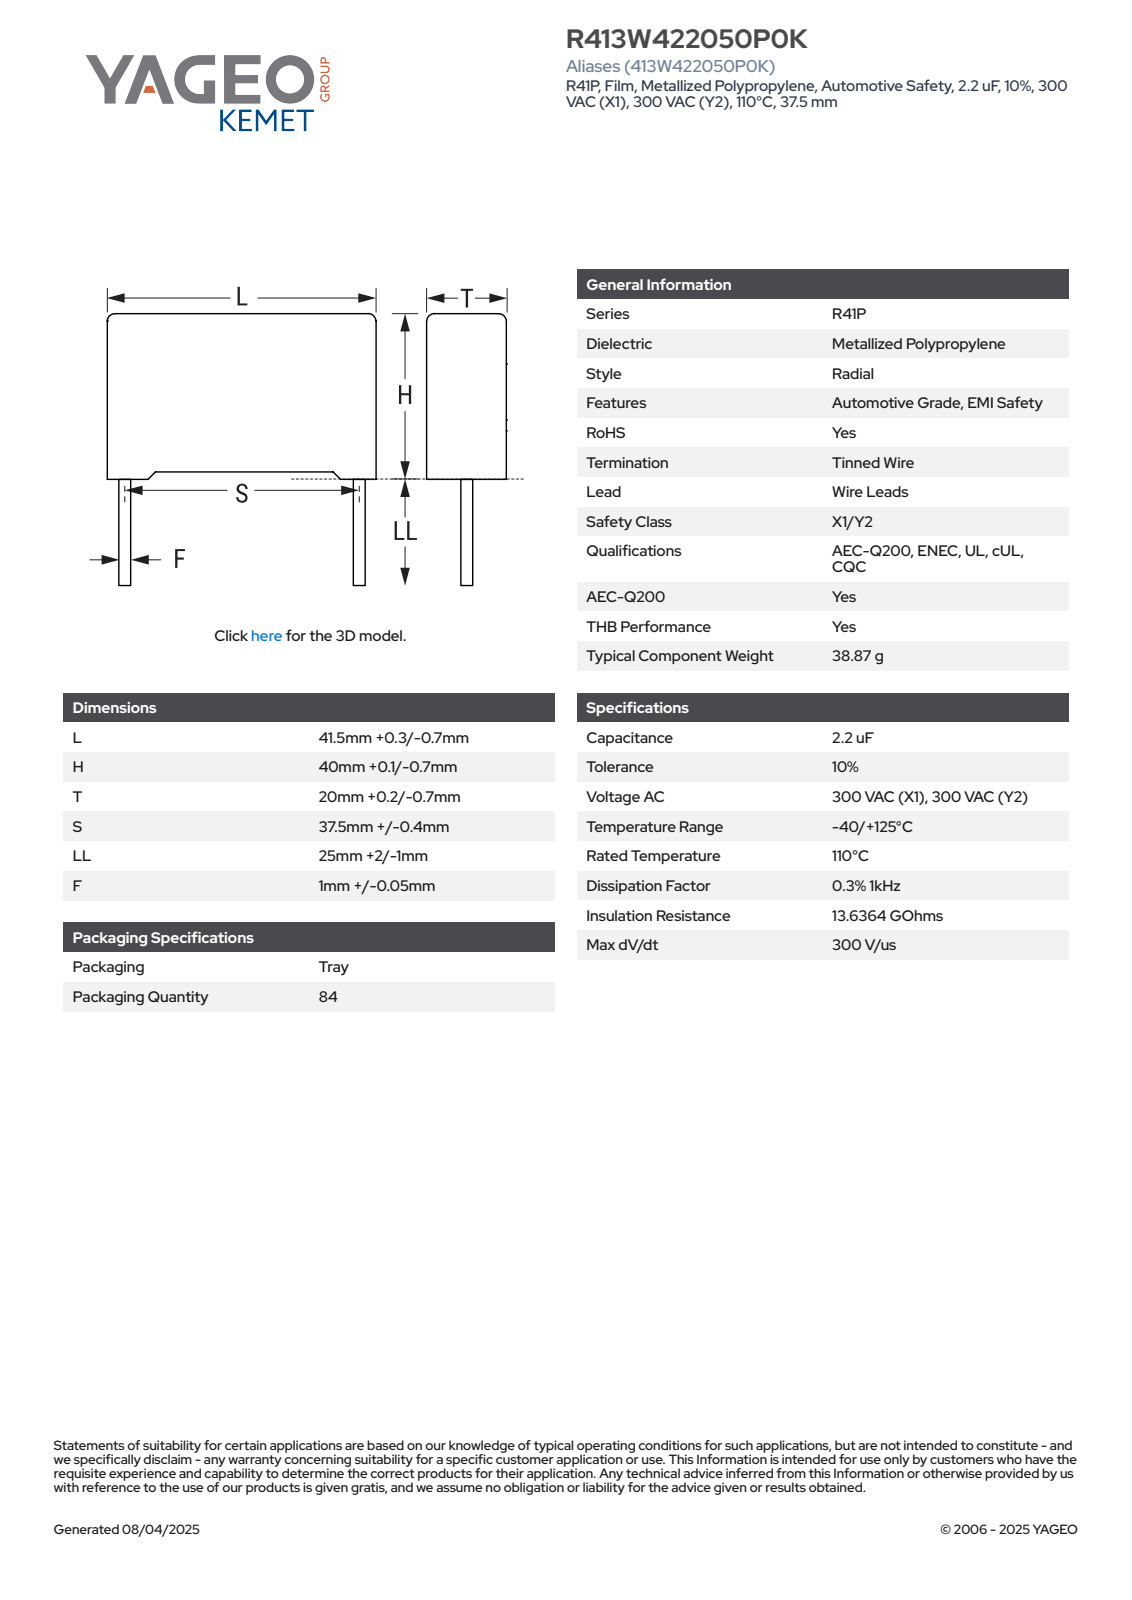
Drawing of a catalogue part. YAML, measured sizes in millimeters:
part_name: "CFR_RB2_41.5X40X2_L41.8H40.1T20.2S37.5LL27F1.05"
step_written_by: "SolidWorks 2021 (AUTOMOTIVE_DESIGN)"
units: millimeters
bodies: {solids: 4, faces: 85, planar: 77, cylindrical: 8, other: 0}
overall_size: [67.1, 41.8, 20.2]
volume: 32902
surface_area: 6904
round_bosses_or_shafts:
  - {diameter: 1.05, count: 2}
partial_cylinders:
  - {radius: 0.5, count: 4}
face_to_face_distances: [20.2, 41.8, 38.72, 0.63, 39.35, 0.75, 1.38, 40.1, 1.39, 20.21]
